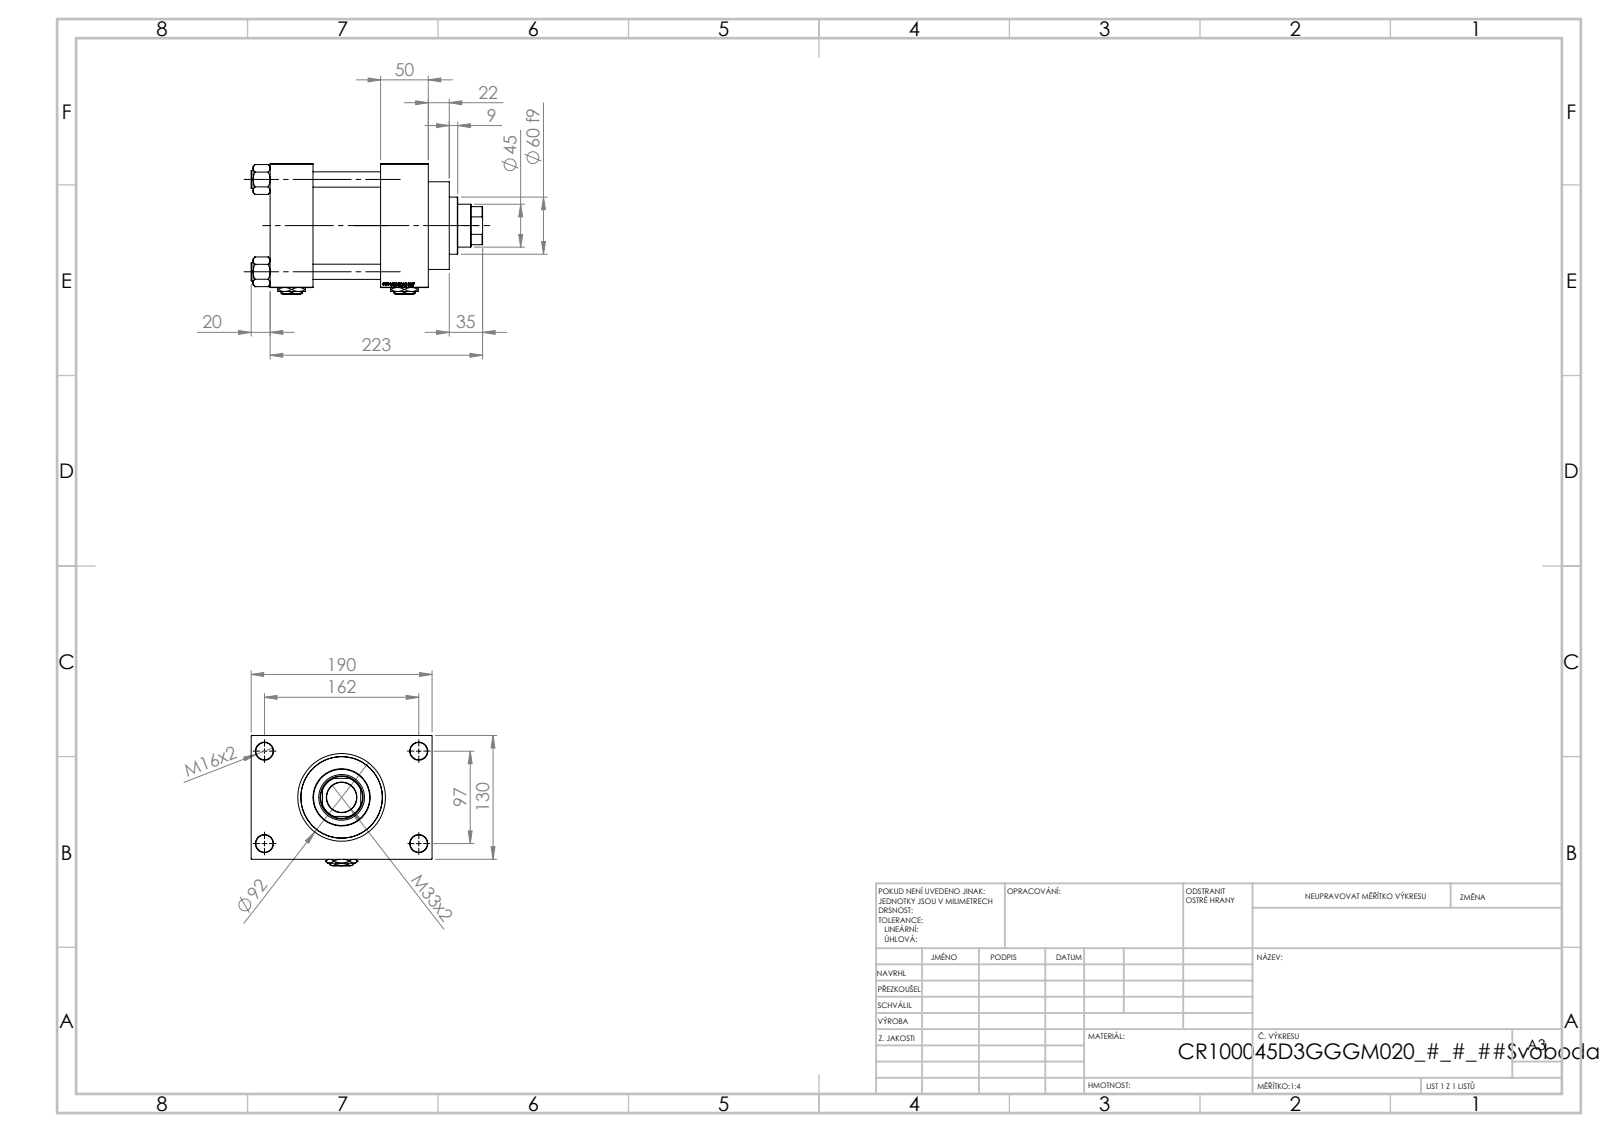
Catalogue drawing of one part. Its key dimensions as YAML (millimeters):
part_name: "V215CR_D_Body; V215CR_VCP_D; V215_VC_A; V215CR_D_TYCINKA (+2 more)"
step_written_by: "SolidWorks 2019 (CONFIG_CONTROL_DESIGN)"
units: millimeters
bodies: {solids: 13, faces: 1253, planar: 593, cylindrical: 100, other: 560}
overall_size: [243, 190, 137]
volume: 2592000
surface_area: 359312
round_holes:
  - {diameter: 16, count: 4}
  - {diameter: 18, count: 4}
  - {diameter: 7, count: 2}
  - {diameter: 26.44, count: 2}
  - {diameter: 35, count: 2}
  - {diameter: 31.5, count: 1}
  - {diameter: 45, count: 1}
  - {diameter: 48, count: 1}
  - {diameter: 76, count: 1}
  - {diameter: 85.5, count: 1}
  - {diameter: 100, count: 1}
round_bosses_or_shafts:
  - {diameter: 19, count: 4}
  - {diameter: 106, count: 1}
  - {diameter: 92, count: 1}
  - {diameter: 60, count: 1}
partial_cylinders:
  - {radius: 22, count: 1}
face_to_face_distances: [130, 45, 116, 71, 166, 121, 50, 160, 30, 20]
hole_center_spacings: [32.55, 68.52, 94.41, 96.9, 102.27, 129.45, 161.73, 97]
